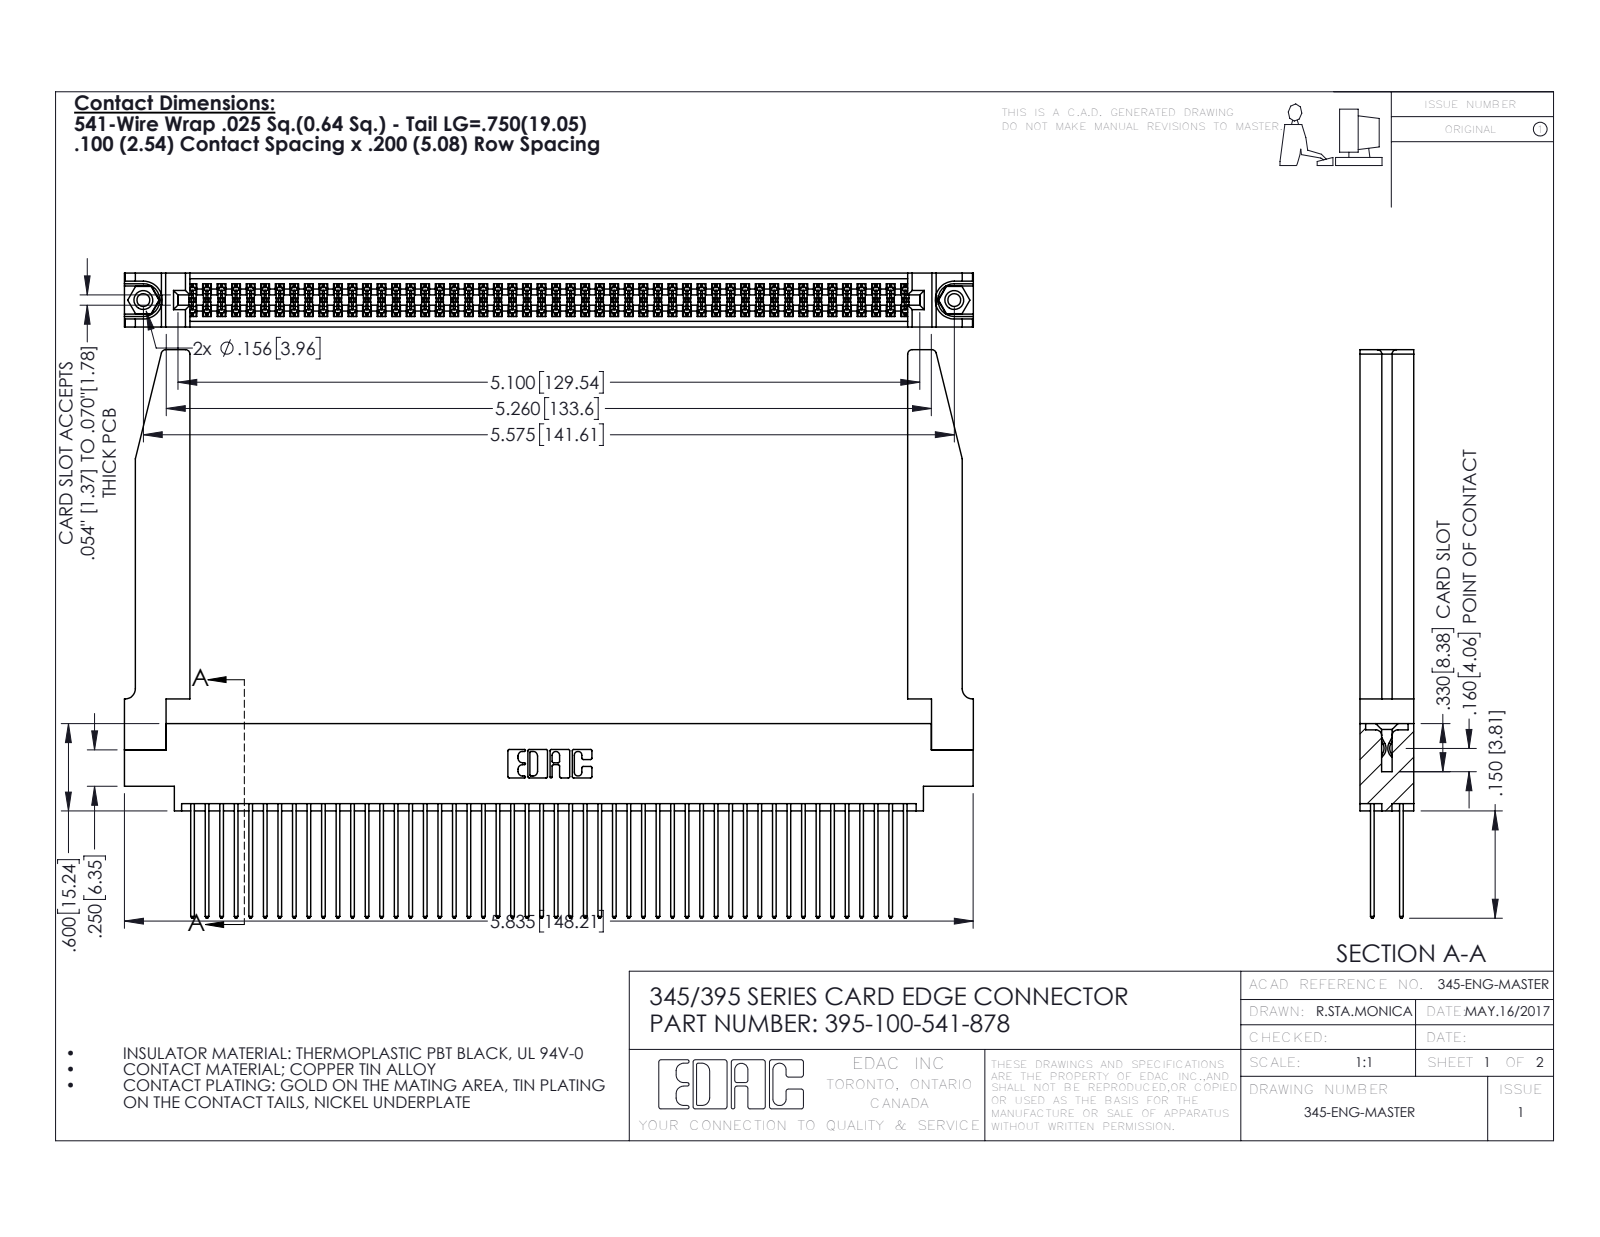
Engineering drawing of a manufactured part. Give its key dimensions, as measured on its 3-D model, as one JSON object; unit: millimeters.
{"part_name": "345-250-001_345-250-001-102; 345-220-078_345-220-078; 345-292-001_345-293-141; 345 Part_0.170 Offset - 0.156 Dia-TH (+1 more)", "step_written_by": "SolidWorks 2016 (CONFIG_CONTROL_DESIGN)", "units": "millimeters", "bodies": {"solids": 105, "faces": 5364, "planar": 3526, "cylindrical": 1786, "other": 52}, "overall_size": [148.2, 99.2, 9.4], "volume_mm3": 22710, "surface_area_mm2": 31910, "round_holes": [[2.3, 2], [3.2, 2], [4, 2], [1.6, 1]], "round_bosses_or_shafts": [[3.9, 2]], "partial_cylinders_radius": [[0.2, 150], [0.3, 100], [0.3, 22], [0.8, 8], [0.2, 6], [0.8, 6], [0.7, 3], [0.4, 2]], "face_to_face_distances": [1.8, 7.6, 9.4, 2.5, 6.9, 0.6, 5.1, 5.7, 4.4, 3.8], "hole_center_spacings": [6.9, 135.6, 141.6]}
